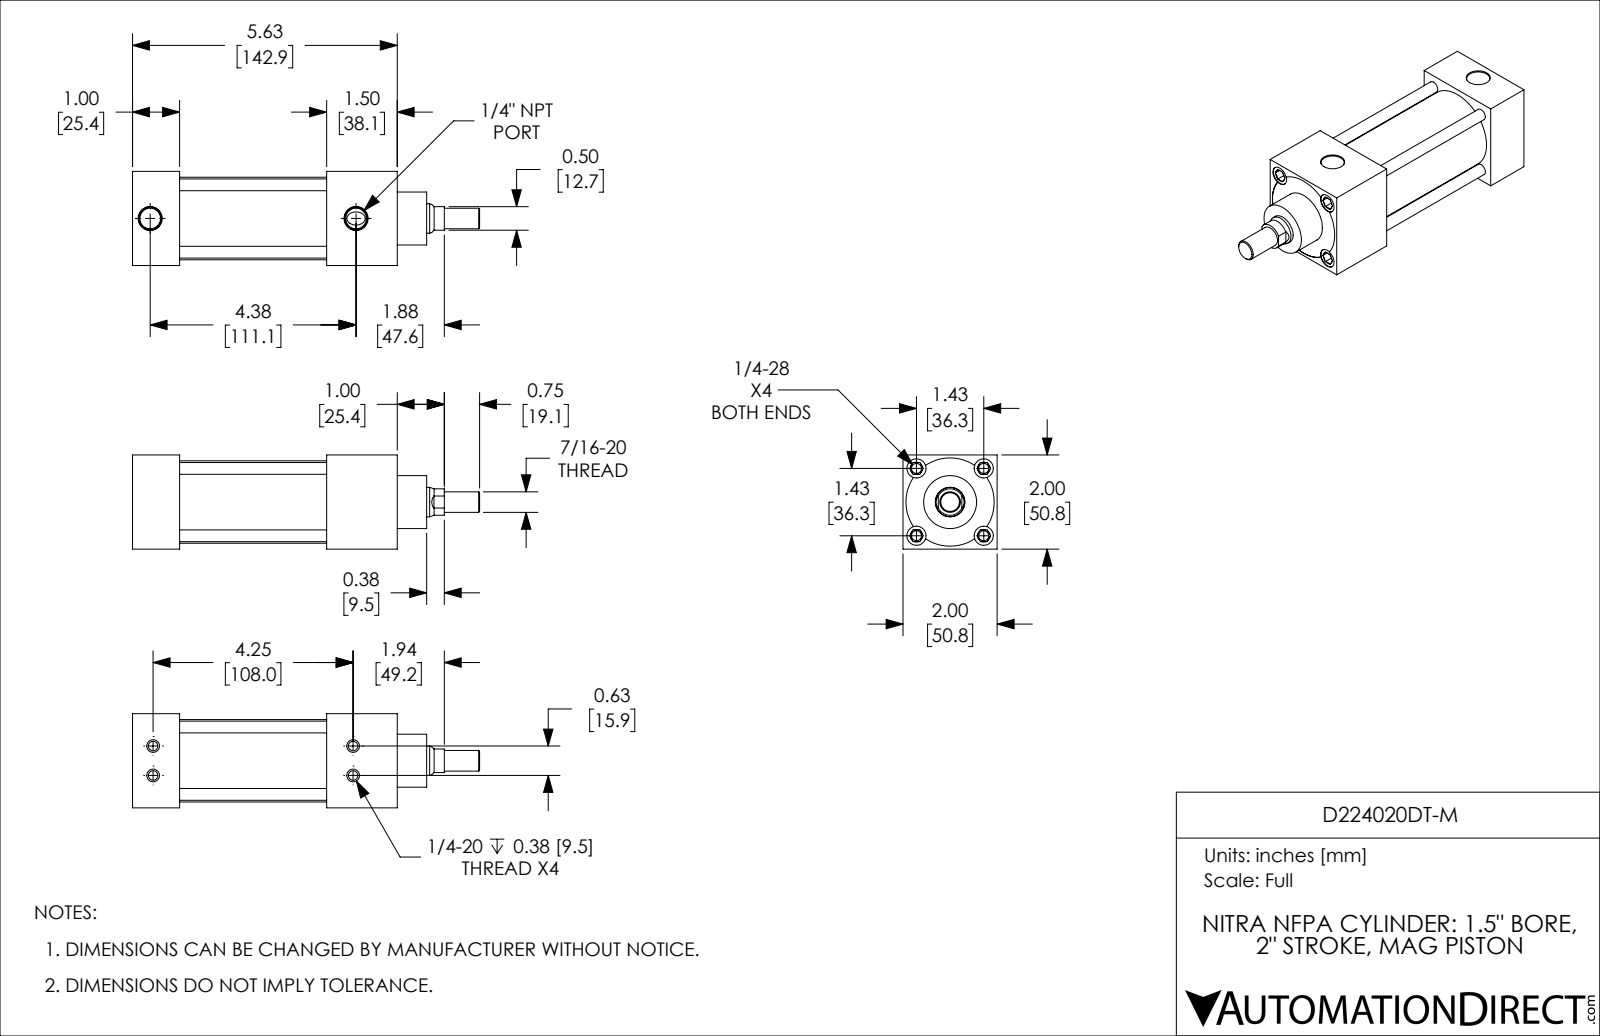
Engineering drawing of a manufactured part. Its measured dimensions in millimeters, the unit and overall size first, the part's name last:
Units: millimetres
Overall size (bounding box): 187.3 × 50.8 × 50.8
Round holes (diameter × count): ⌀5.1 ×4, ⌀5.4 ×4, ⌀10.3 ×4, ⌀11.1 ×2, ⌀15.9 ×1, ⌀38.1 ×1
Round bosses / shafts (diameter × count): ⌀6.4 ×4, ⌀44.5 ×1, ⌀38.1 ×1, ⌀28.6 ×1, ⌀15.8 ×1, ⌀11.1 ×1
Partial cylindrical surfaces — rounded edges, fillets, slot ends (radius × count): R7.1 ×1, R23.8 ×1
Main face-to-face distances: 50.8, 25.4, 104.8, 79.4, 142.7, 117.3, 38, 54, 28.6, 88.8
Hole centre spacings: 8.1, 25.7, 36.3, 15.9, 51.4, 108, 109.1, 109.8
Volume: 253 300 mm³ · Surface area: 69 610 mm²
Bodies: 2 solids, 203 faces (58 planar, 65 cylindrical, 80 other)
Part name (STEP PRODUCT): D224020DT-M_BODY; D224020DT-M_PISTON_KK1; D224020DT-M
STEP written by: SolidWorks 2019 (CONFIG_CONTROL_DESIGN)
